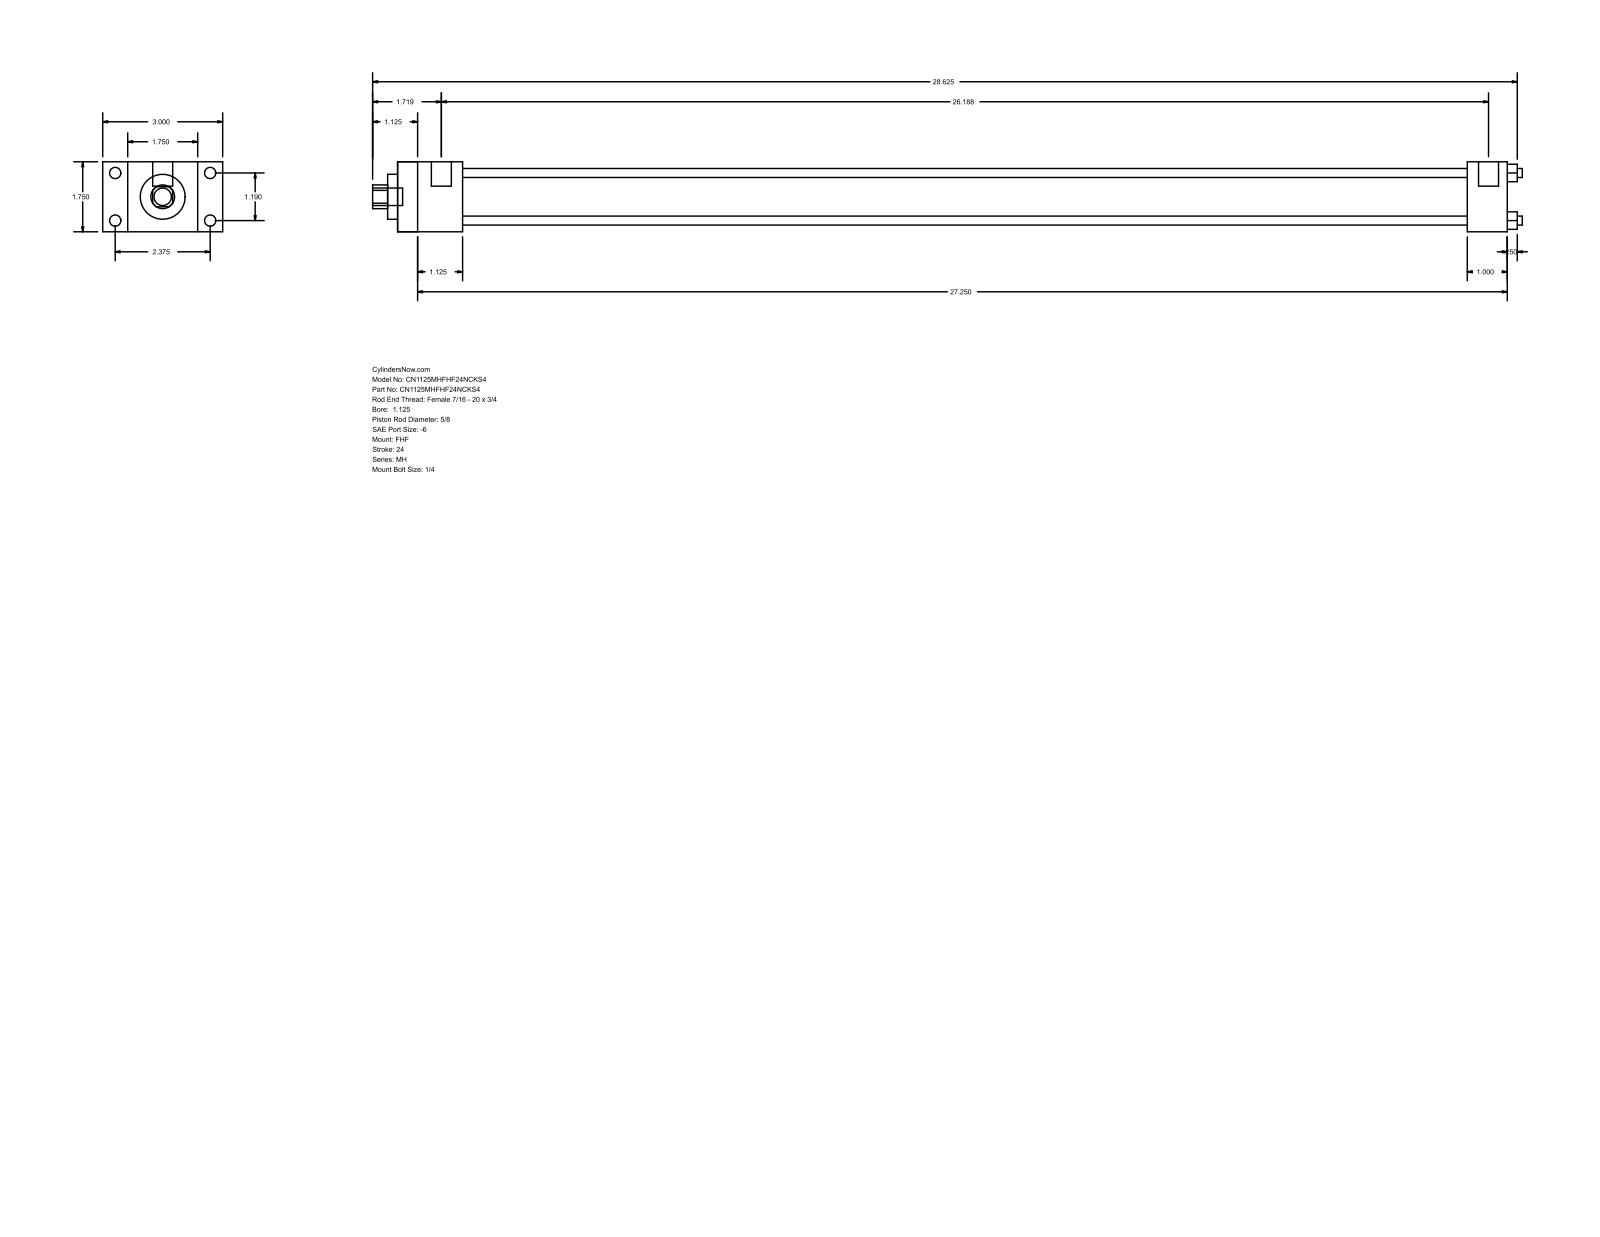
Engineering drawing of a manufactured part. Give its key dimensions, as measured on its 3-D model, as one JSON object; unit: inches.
{"part_name": "MH_FHF__0112_0.625", "step_written_by": "GSSL Pune (CONFIG_CONTROL_DESIGN)", "units": "inches", "bodies": {"solids": 0, "faces": 88, "planar": 60, "cylindrical": 28, "other": 0}, "overall_size": [28.75, 3, 1.75], "round_holes": [[0.225, 4], [0.625, 1], [1.125, 1], [1.375, 1]], "round_bosses_or_shafts": [[0.281, 4], [0.219, 4], [0.5, 2], [0.437, 1]], "partial_cylinders_radius": [[0.297, 1]], "face_to_face_distances": [1.75, 0.625, 2.375, 1.625, 3, 27.75, 26.125, 26.75, 25.125, 1], "hole_center_spacings": [0.841, 1.19, 1.683]}
